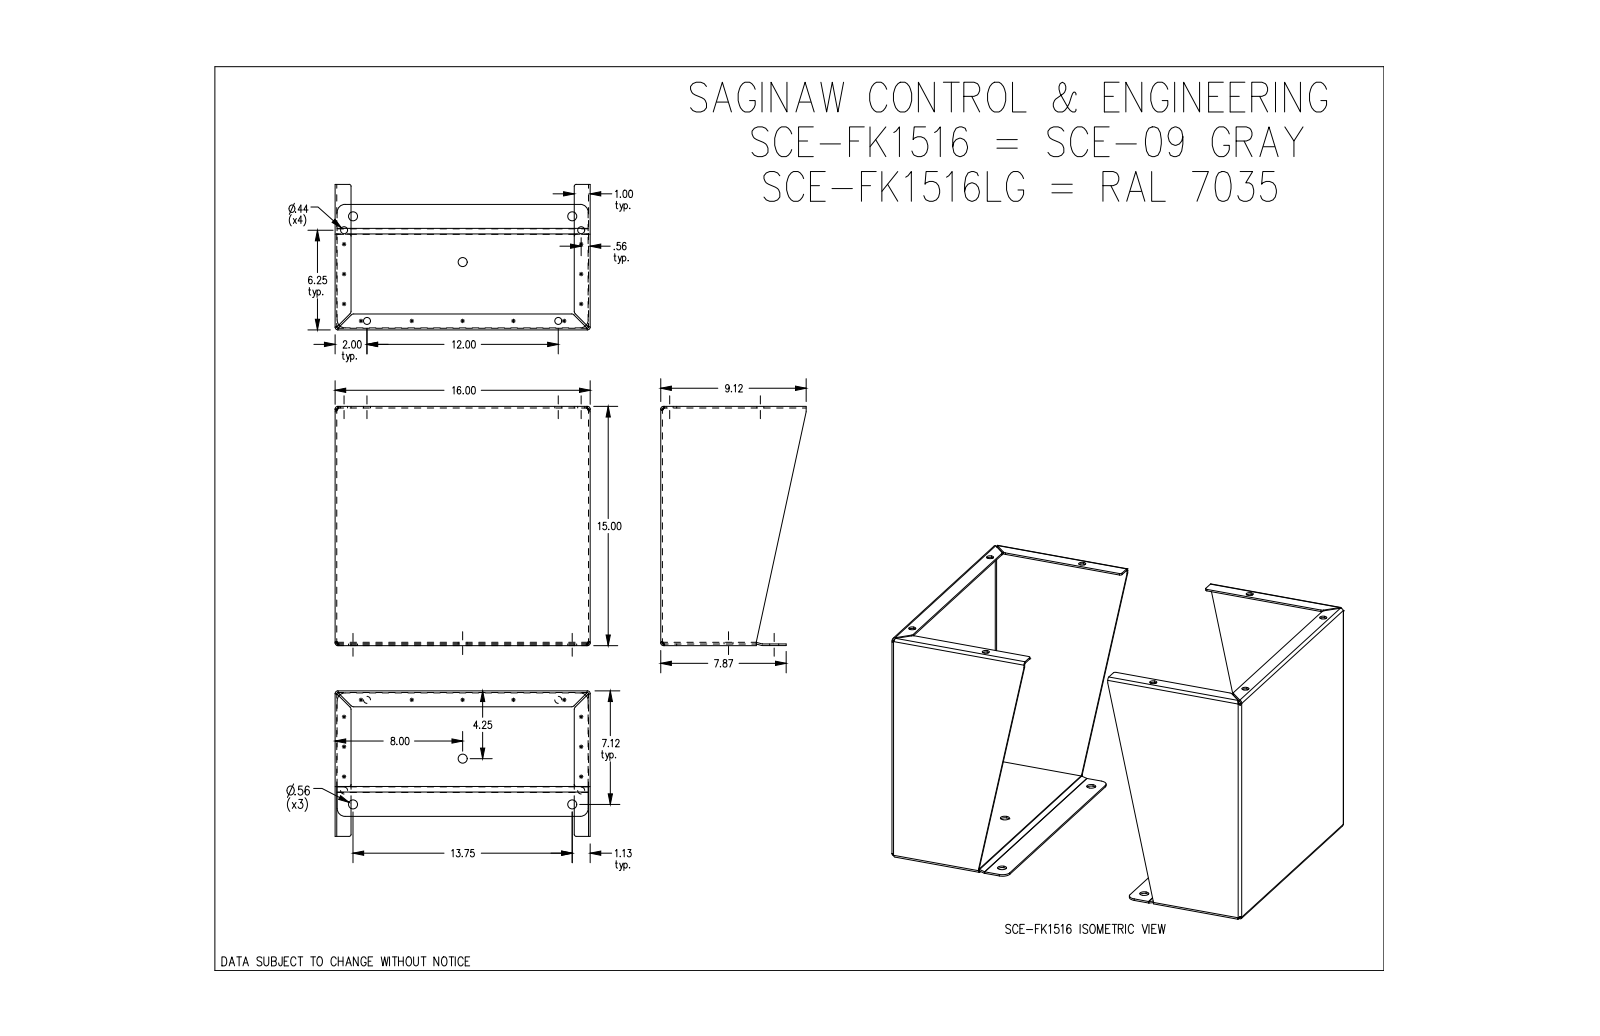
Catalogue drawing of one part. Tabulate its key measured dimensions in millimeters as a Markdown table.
| quantity | value |
| --- | --- |
| part name | SCE-FK1516 |
| STEP written by | SolidWorks 2019 (CONFIG_CONTROL_DESIGN) |
| units | millimeters |
| bodies | 4 solids, 214 faces (96 planar, 86 cylindrical, 32 other) |
| overall size | 609.6 × 406.4 × 381 |
| volume | 2 152 000 mm³ |
| surface area | 1 650 000 mm² |
| round holes (diameter × count) | 11.1 × 8, 14.3 × 6 |
| partial cylindrical surfaces (radius × count) | 4.2 × 16, 1.6 × 12, 3.2 × 8, 5.6 × 8, 12.7 × 8, 1.6 × 6 |
| main face-to-face distances | 2.6, 607, 403.8, 609.6, 604.3, 406.4, 401.1, 375.7, 378.4, 2.6 |
| hole center spacings | 26.3, 149, 168, 178.9, 189.2, 195.6, 270.4, 365.3 |
